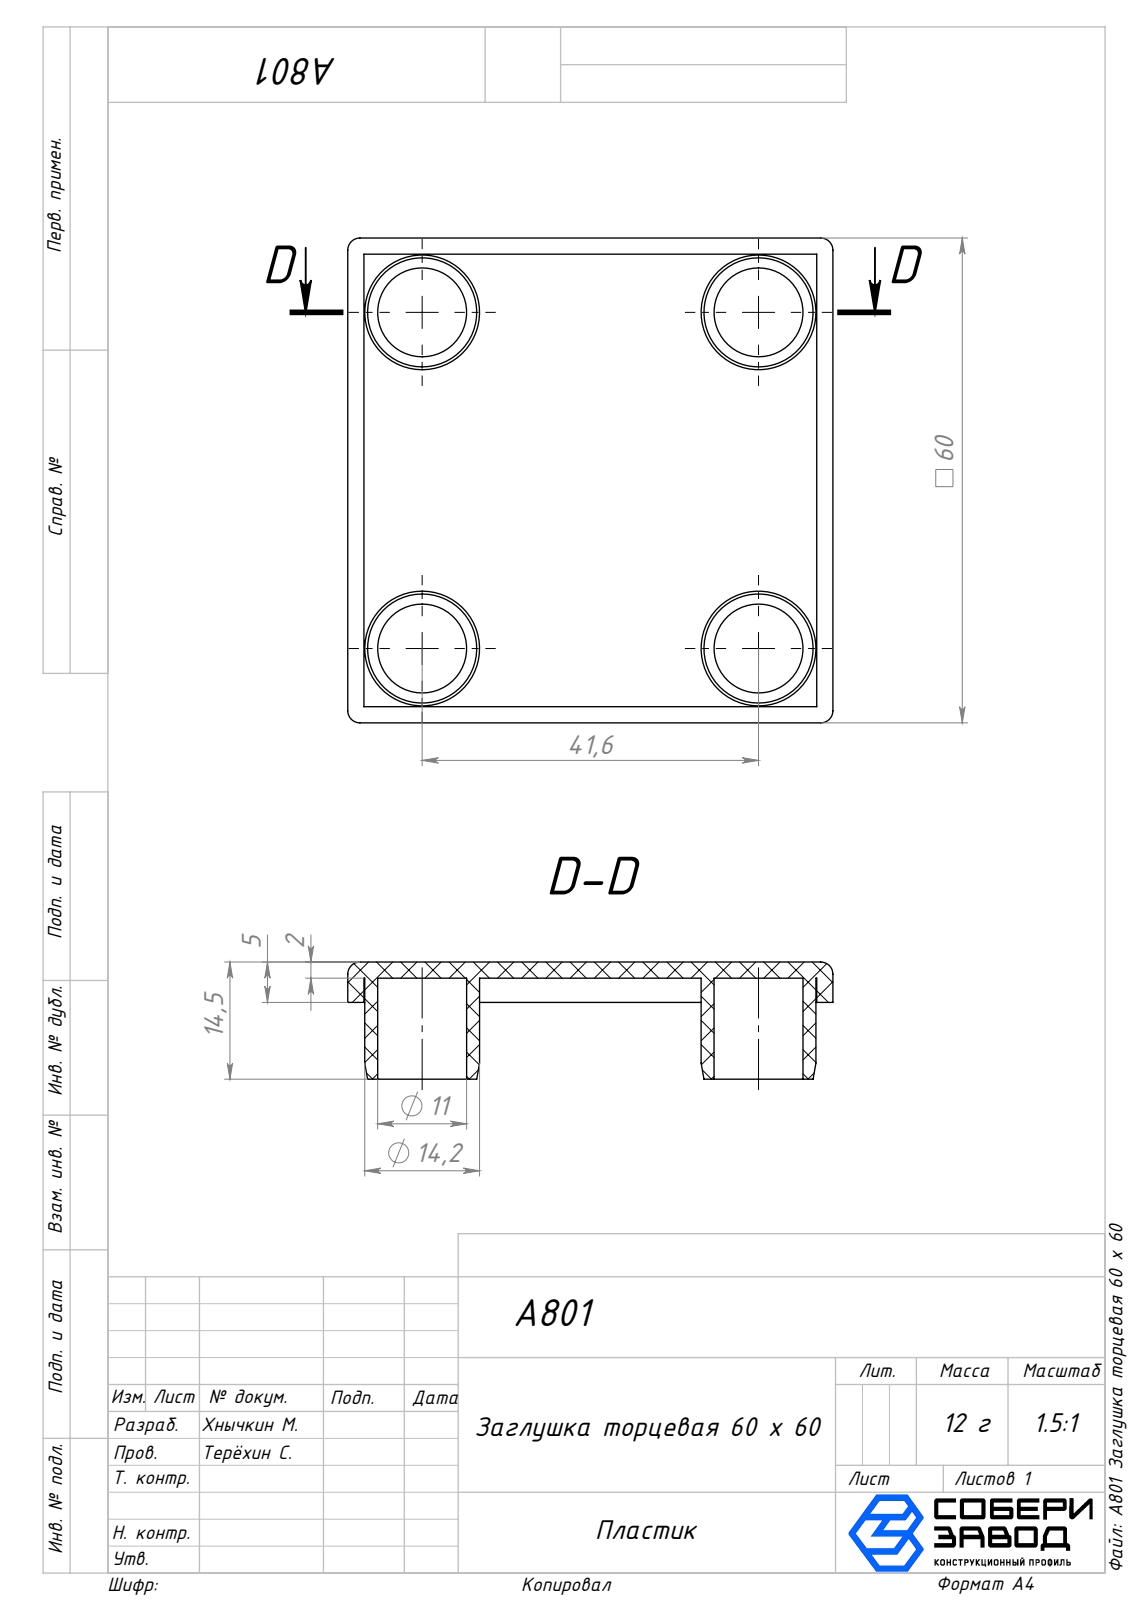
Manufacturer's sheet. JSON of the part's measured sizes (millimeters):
{"part_name": "A801 Заглушка торцевая 60 х 60", "step_written_by": "SolidWorks 2025 (AUTOMOTIVE_DESIGN)", "units": "millimeters", "bodies": {"solids": 1, "faces": 55, "planar": 19, "cylindrical": 24, "other": 12}, "overall_size": [60, 60, 14.5], "volume_mm3": 11574, "surface_area_mm2": 12795, "round_holes": [[11, 4]], "round_bosses_or_shafts": [[14.2, 4]], "partial_cylinders_radius": [[1.5, 8]], "face_to_face_distances": [2, 58, 5, 3, 60, 56, 14.5, 12.5, 9.5], "hole_center_spacings": [41.6, 58.83]}
